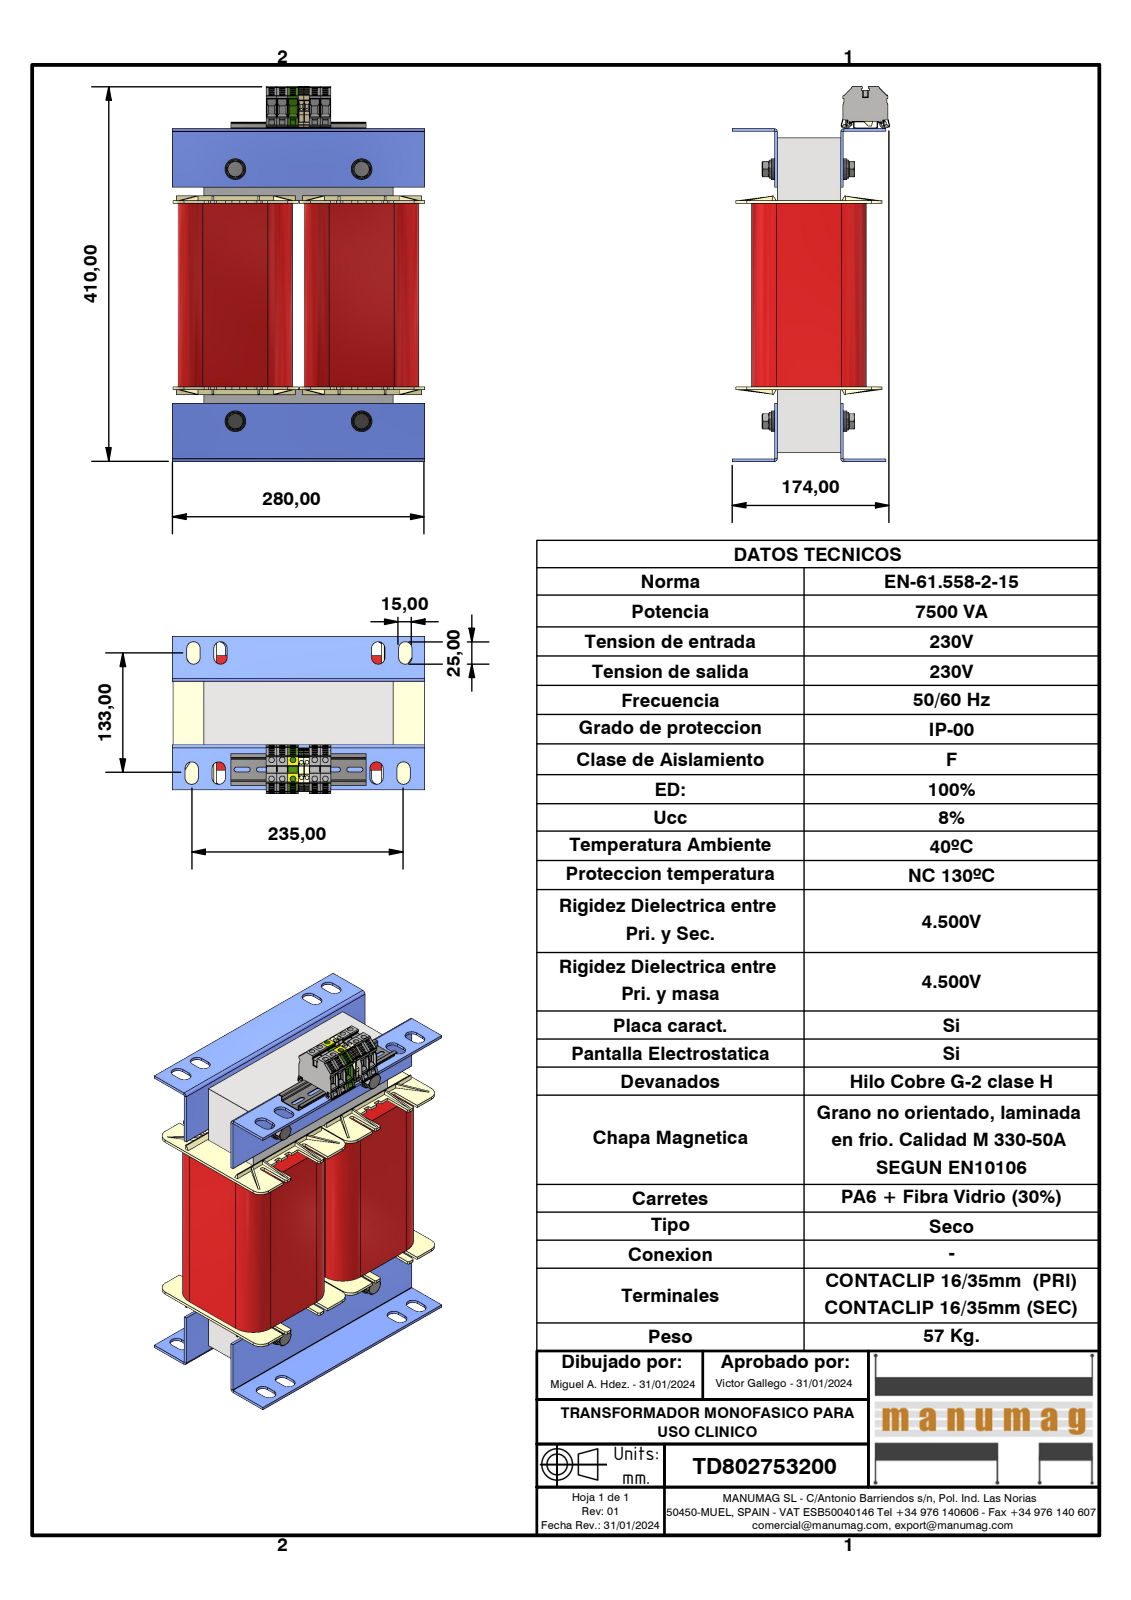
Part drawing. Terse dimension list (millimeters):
name: TD802753200; UI350 x 210 - 70 (Rc70); UI 210_70_BOBINADO; RC 70 UI (+8 more)
written by: Autodesk Inventor 2023 (AUTOMOTIVE_DESIGN)
unit: mm
bodies: 39 solids, 3704 faces (2314 planar, 1124 cylindrical, 266 other)
size: 417.1 × 280 × 174.4
volume: 9 033 000 mm³; area: 1 277 000 mm²
holes: 10× ⌀6.3, 4× ⌀4.3, 4× ⌀8.38, 4× ⌀10.5, 4× ⌀14, 4× ⌀16, 2× ⌀2.4, 2× ⌀2.5, 2× ⌀2.75, 2× ⌀2.95
bosses: 4× ⌀23, 4× ⌀20, 4× ⌀15.4, 4× ⌀14.7, 4× ⌀10, 4× ⌀9.19
rounds: 263× R0.3, 32× R0.25, 32× R7.5, 27× R2, 18× R1, 16× R2.5, 13× R0.5, 12× R2.6
face distances: 3, 73, 70, 0.5, 73.5, 140, 3.5, 25, 25.5, 28.5
hole spacings: 11.9, 24.14, 21, 36, 41.68, 47.9, 52.3, 6.1
